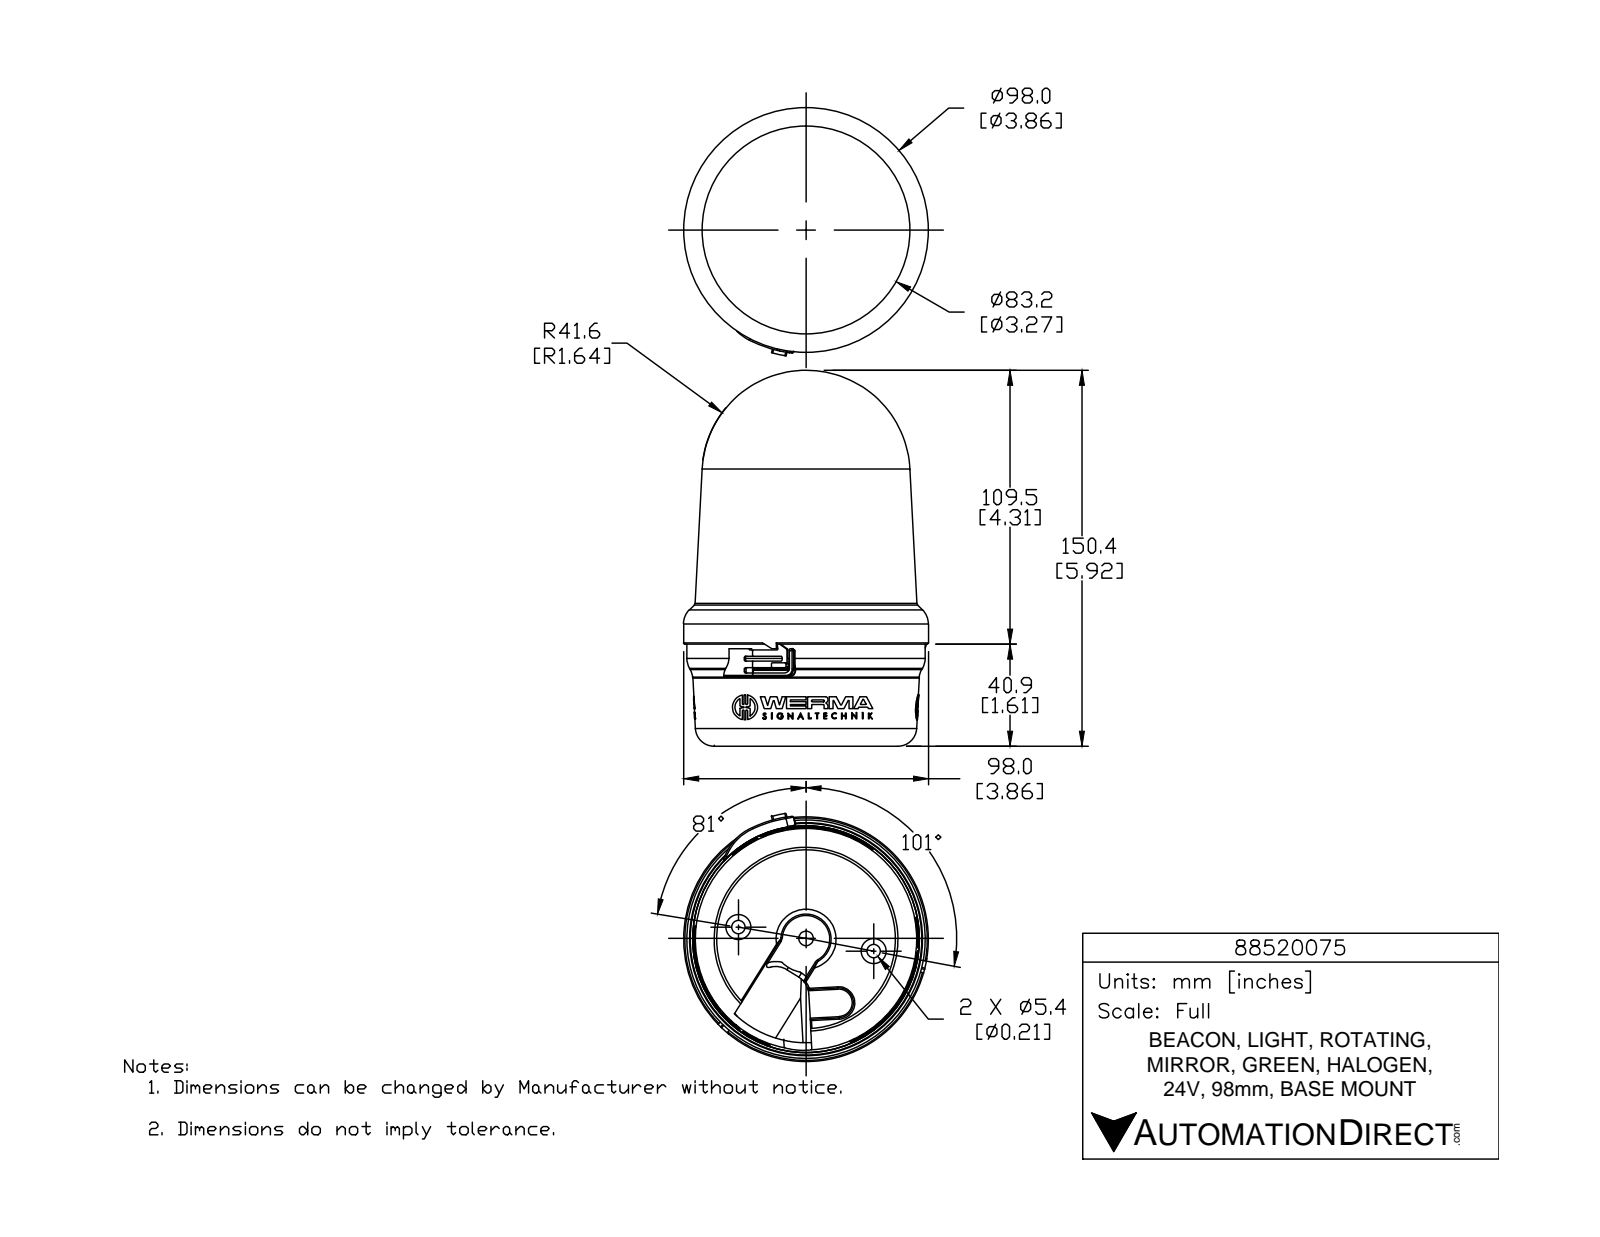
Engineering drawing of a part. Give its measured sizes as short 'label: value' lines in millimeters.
name: 88520075
written by: SolidWorks 2015 (AUTOMOTIVE_DESIGN)
unit: mm
bodies: 1 solid, 969 faces (586 planar, 238 cylindrical, 145 other)
size: 150.4 × 99.4 × 98
volume: 811 300 mm³; area: 52 970 mm²
holes: 3× ⌀1.7, 2× ⌀5.4, 2× ⌀10.4, 1× ⌀71.5
bosses: 3× ⌀10, 3× ⌀2.5, 2× ⌀10, 1× ⌀98, 1× ⌀95.4, 1× ⌀90.7
rounds: 21× R0.5, 9× R0.2, 6× R0.2, 6× R0.4, 6× R0.4, 6× R0.4, 6× R5.8, 4× R2
face distances: 1.5, 0.8, 6.9, 0.5, 7.3, 18.6, 19.5, 8, 33.5, 32
hole spacings: 27.5, 55
